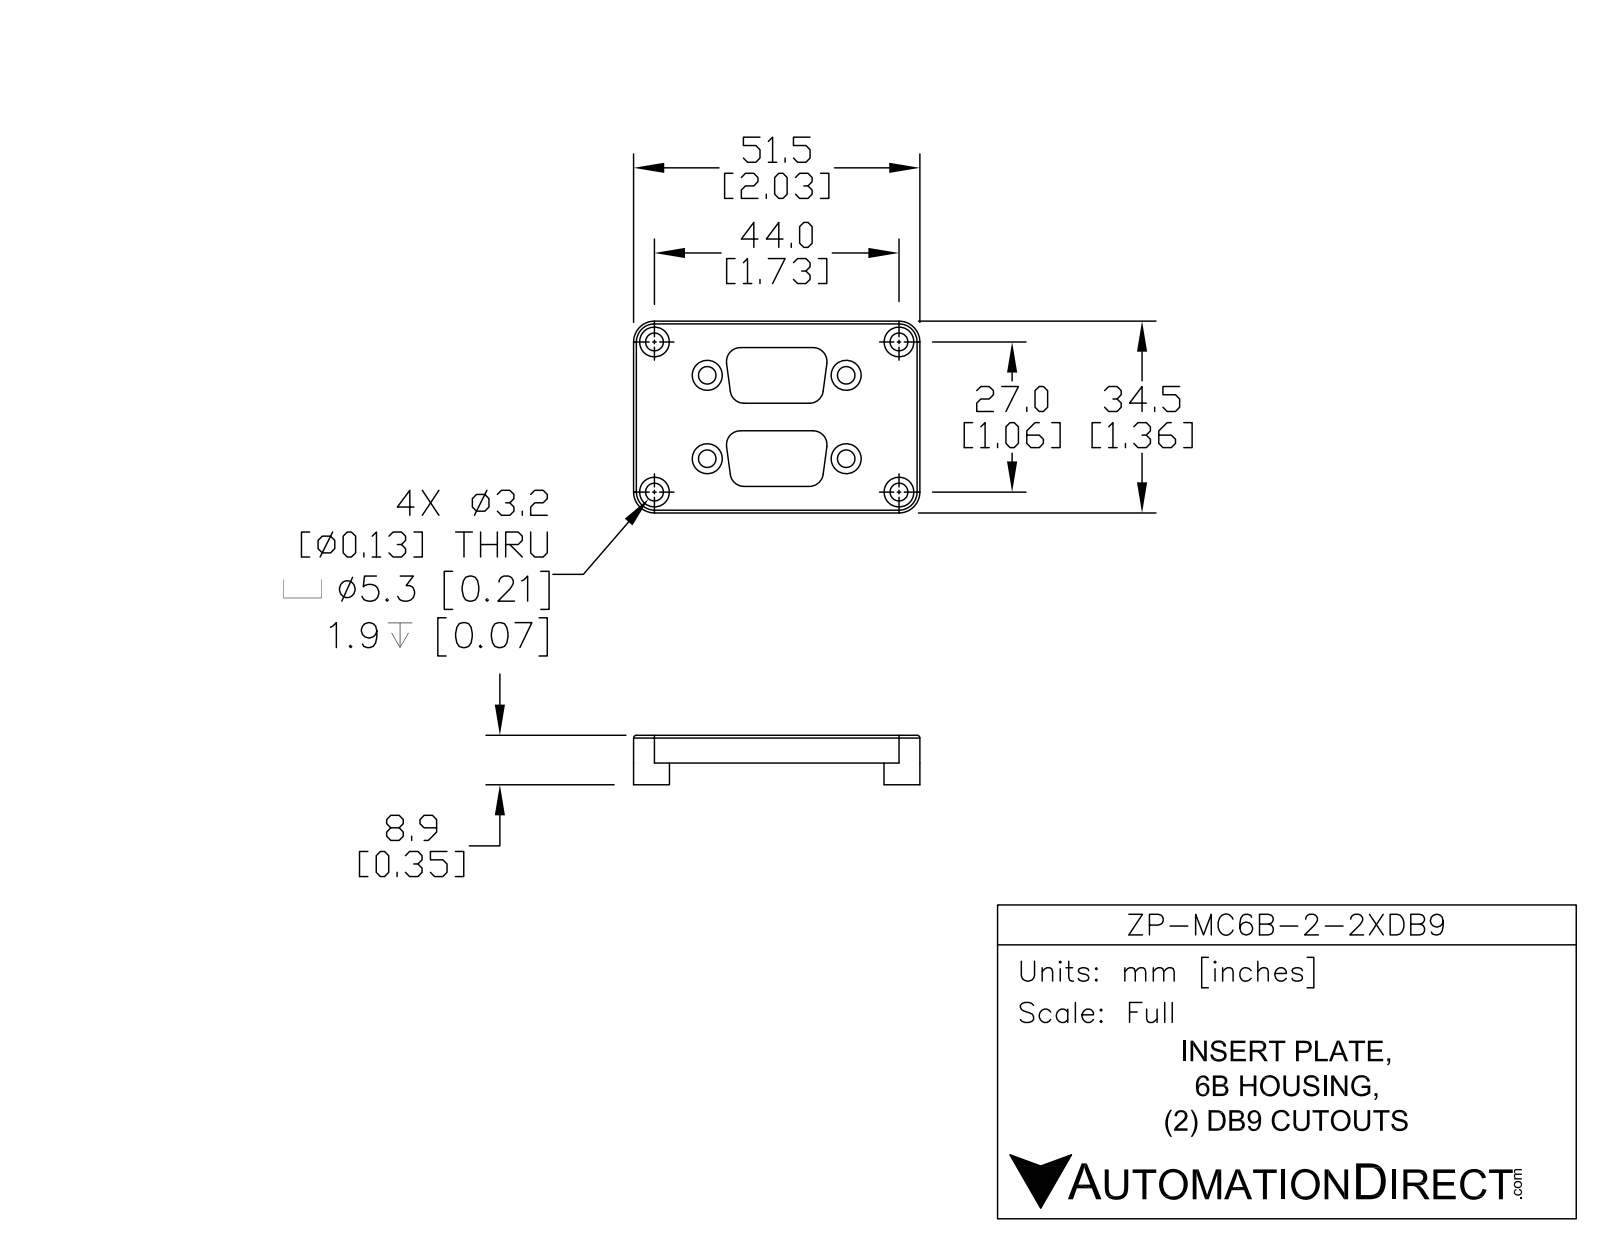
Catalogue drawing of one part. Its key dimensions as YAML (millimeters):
part_name: "ZP-MC6B-2-2XDB9"
step_written_by: "SolidWorks 2014 (AUTOMOTIVE_DESIGN)"
units: millimeters
bodies: {solids: 1, faces: 106, planar: 48, cylindrical: 46, other: 12}
overall_size: [51.5, 34.5, 8.91]
volume: 4548
surface_area: 5003
round_holes:
  - {diameter: 3.15, count: 4}
  - {diameter: 3.21, count: 4}
  - {diameter: 5.35, count: 4}
partial_cylinders:
  - {radius: 2.5, count: 8}
  - {radius: 0.5, count: 4}
  - {radius: 3.75, count: 4}
face_to_face_distances: [2.4, 2.15, 2.6, 2.85, 5, 32.1, 34.5, 27.9, 6.45, 45.05]
hole_center_spacings: [11.24, 23.05, 35.02, 40.39, 15, 25, 27, 29.15]
